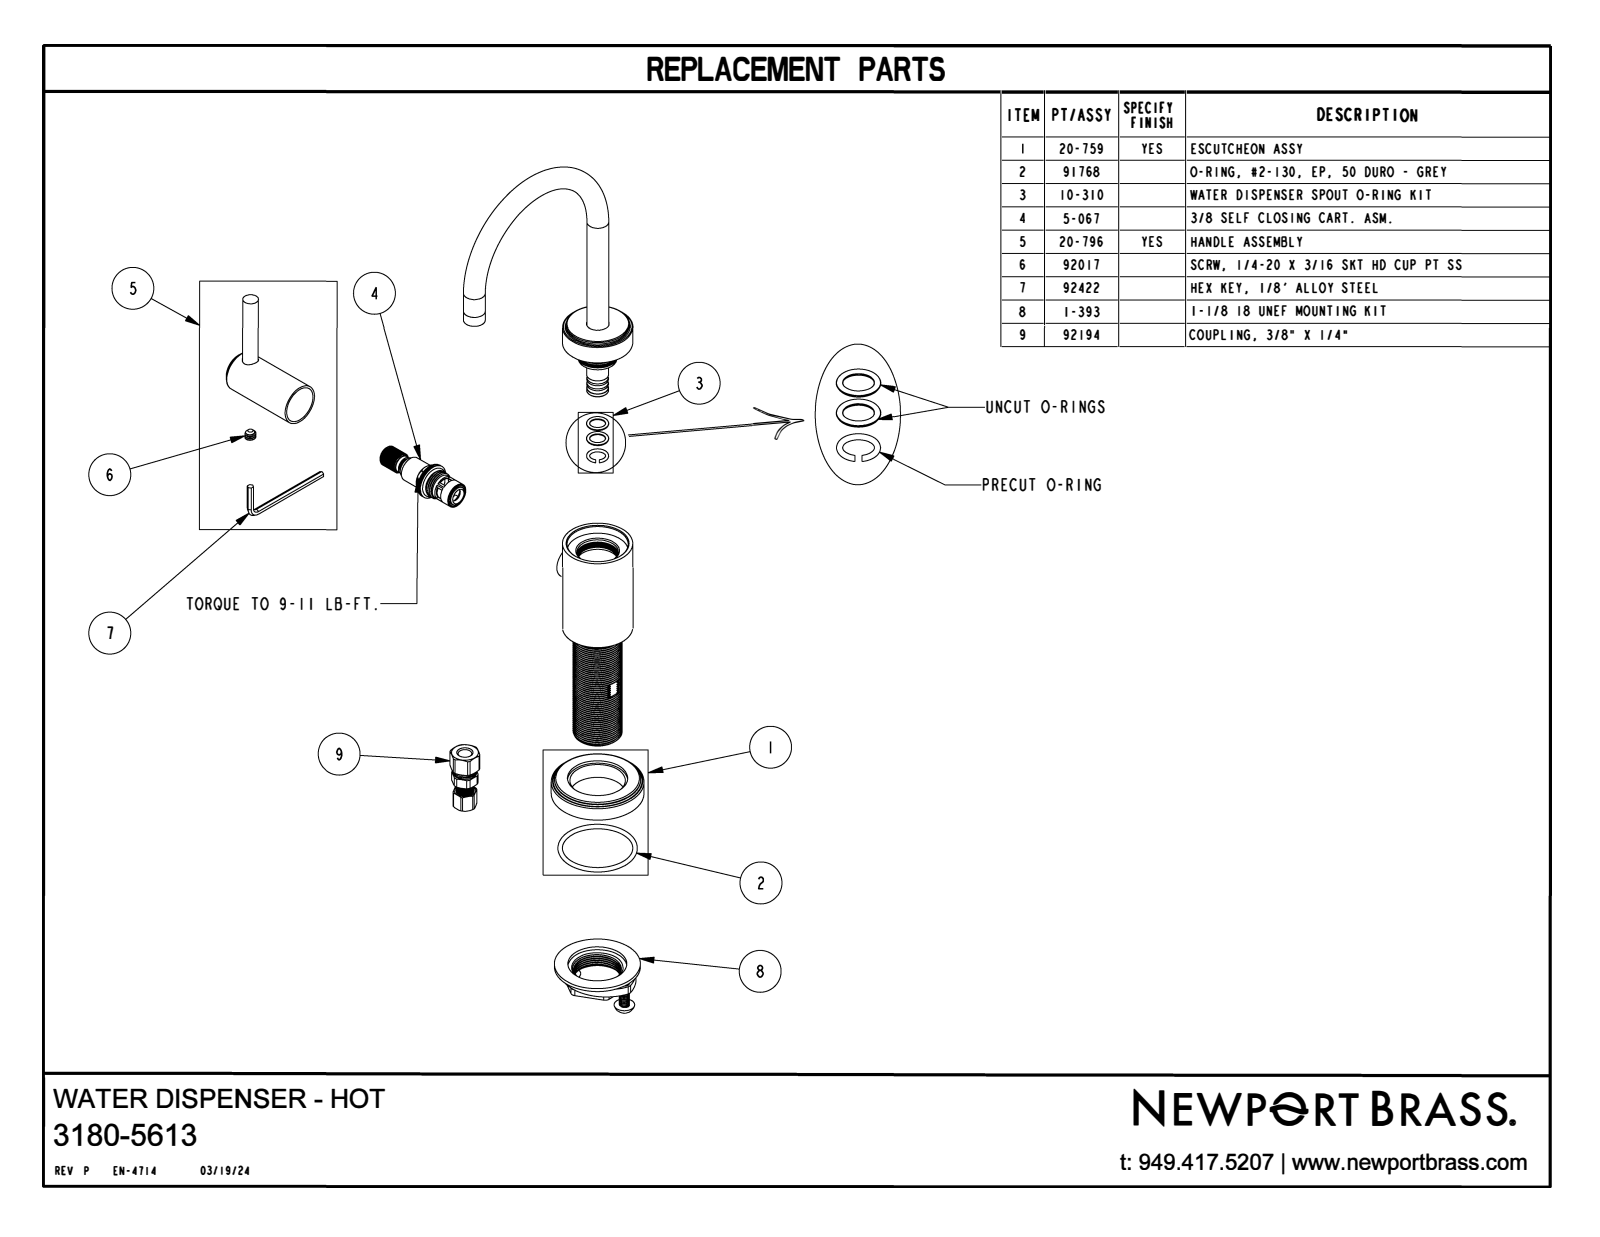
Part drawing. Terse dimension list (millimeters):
name: 3180-5613
written by: CREO PARAMETRIC BY PTC INC, 2018400 (CONFIG_CONTROL_DESIGN)
unit: mm
bodies: 1 solid, 53 faces (11 planar, 22 cylindrical, 20 other)
size: 237.4 × 135 × 92.7
volume: 177 300 mm³; area: 31 730 mm²
holes: 1× ⌀9.5, 1× ⌀25.4
bosses: 2× ⌀12.7, 1× ⌀54, 1× ⌀50.2, 1× ⌀40.9, 1× ⌀36.8, 1× ⌀24.1, 1× ⌀20.3, 1× ⌀9.1
face distances: 84, 10.8, 73.2, 167.6, 156.8, 83.6, 82, 71.2, 2, 85.6
